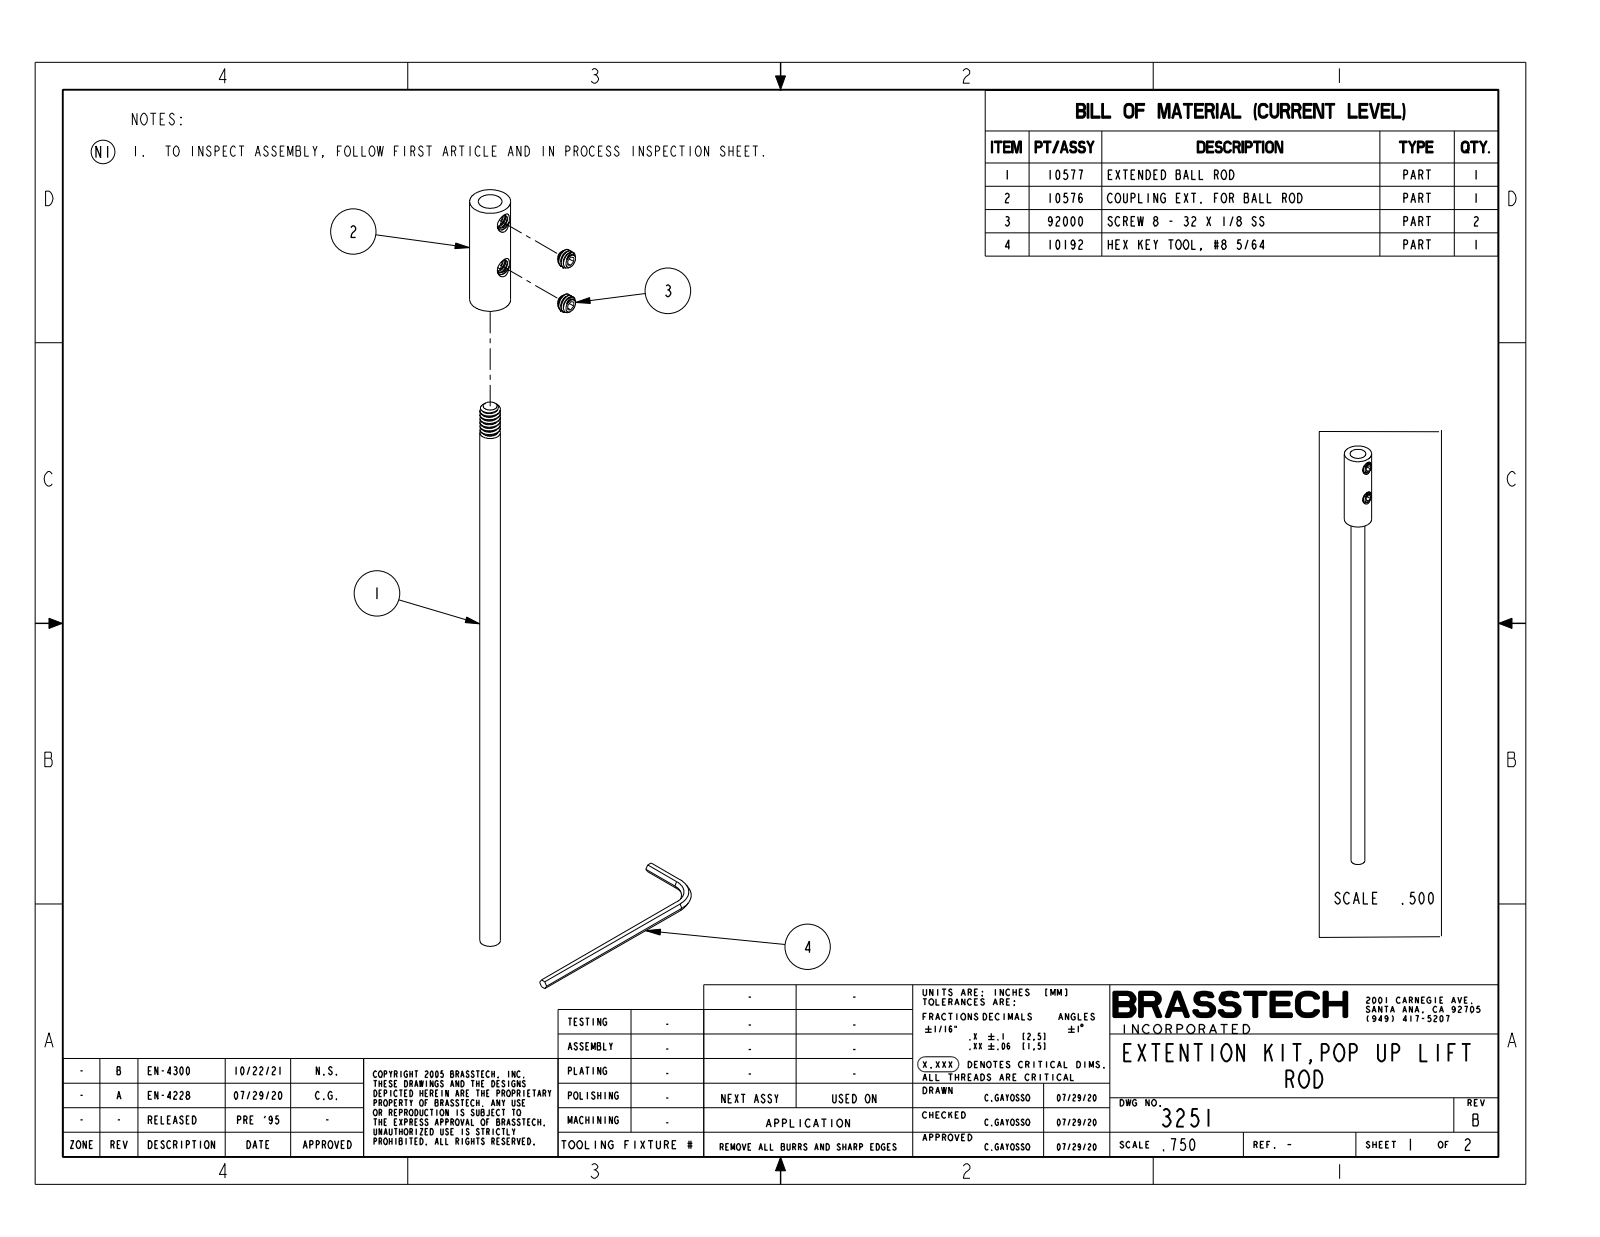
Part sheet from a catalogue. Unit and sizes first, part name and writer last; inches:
Units: inches
Overall size (bounding box): 6.85 × 0.388 × 0.375
Round holes (diameter × count): ⌀0.13 ×2, ⌀0.216 ×1
Round bosses / shafts (diameter × count): ⌀0.164 ×2, ⌀0.375 ×1, ⌀0.187 ×1, ⌀0.145 ×1
Partial cylindrical surfaces — rounded edges, fillets, slot ends (radius × count): R0.08 ×2
Main face-to-face distances: 1.1, 5.75, 6.85, 6.05, 0.3, 0.8, 0.433, 0.08, 0.05, 6
Hole centre spacings: 0.5
Volume: 0.246 in³ · Surface area: 11.68 in²
Bodies: 1 solid, 178 faces (45 planar, 42 cylindrical, 91 other)
Part name (STEP PRODUCT): 3251
STEP written by: CREO PARAMETRIC BY PTC INC, 2018500 (CONFIG_CONTROL_DESIGN)
